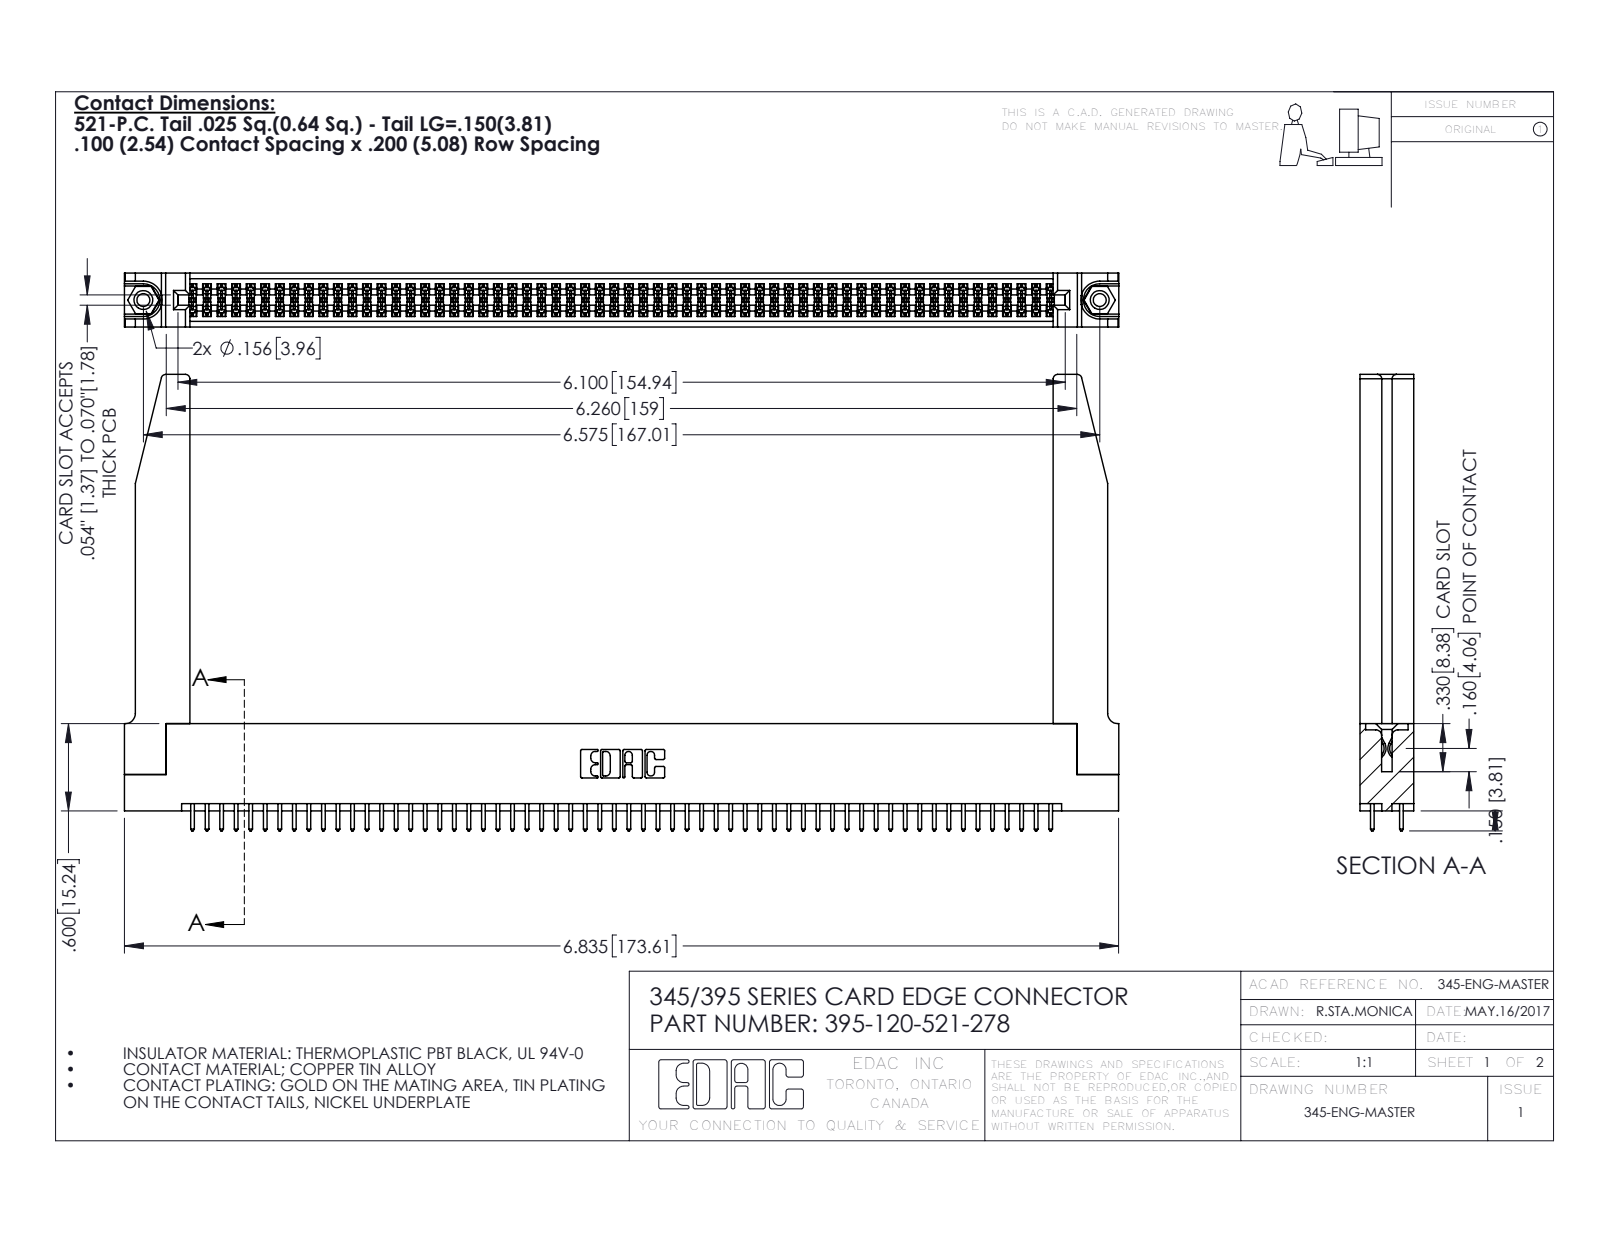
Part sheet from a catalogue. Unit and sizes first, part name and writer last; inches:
Units: inches
Overall size (bounding box): 6.836 × 3.137 × 0.37
Round holes (diameter × count): ⌀0.089 ×2, ⌀0.125 ×2, ⌀0.156 ×2, ⌀0.064 ×1
Round bosses / shafts (diameter × count): ⌀0.155 ×2
Partial cylindrical surfaces — rounded edges, fillets, slot ends (radius × count): R0.006 ×180, R0.01 ×120, R0.01 ×22, R0.03 ×8, R0.007 ×6, R0.031 ×6, R0.026 ×3, R0.014 ×2
Main face-to-face distances: 0.072, 0.298, 0.37, 0.2, 0.098, 0.272, 0.025, 0.225, 0.175, 0.148
Hole centre spacings: 0.27, 6.339, 6.575
Volume: 1.511 in³ · Surface area: 49.56 in²
Bodies: 125 solids, 6360 faces (4182 planar, 2126 cylindrical, 52 other)
Part name (STEP PRODUCT): 395-120-521-278; 345-220-078_345-220-078; 345-250-001_345-250-001-102; 345-292-001_345-293-121 (+1 more)
STEP written by: SolidWorks 2016 (CONFIG_CONTROL_DESIGN)
